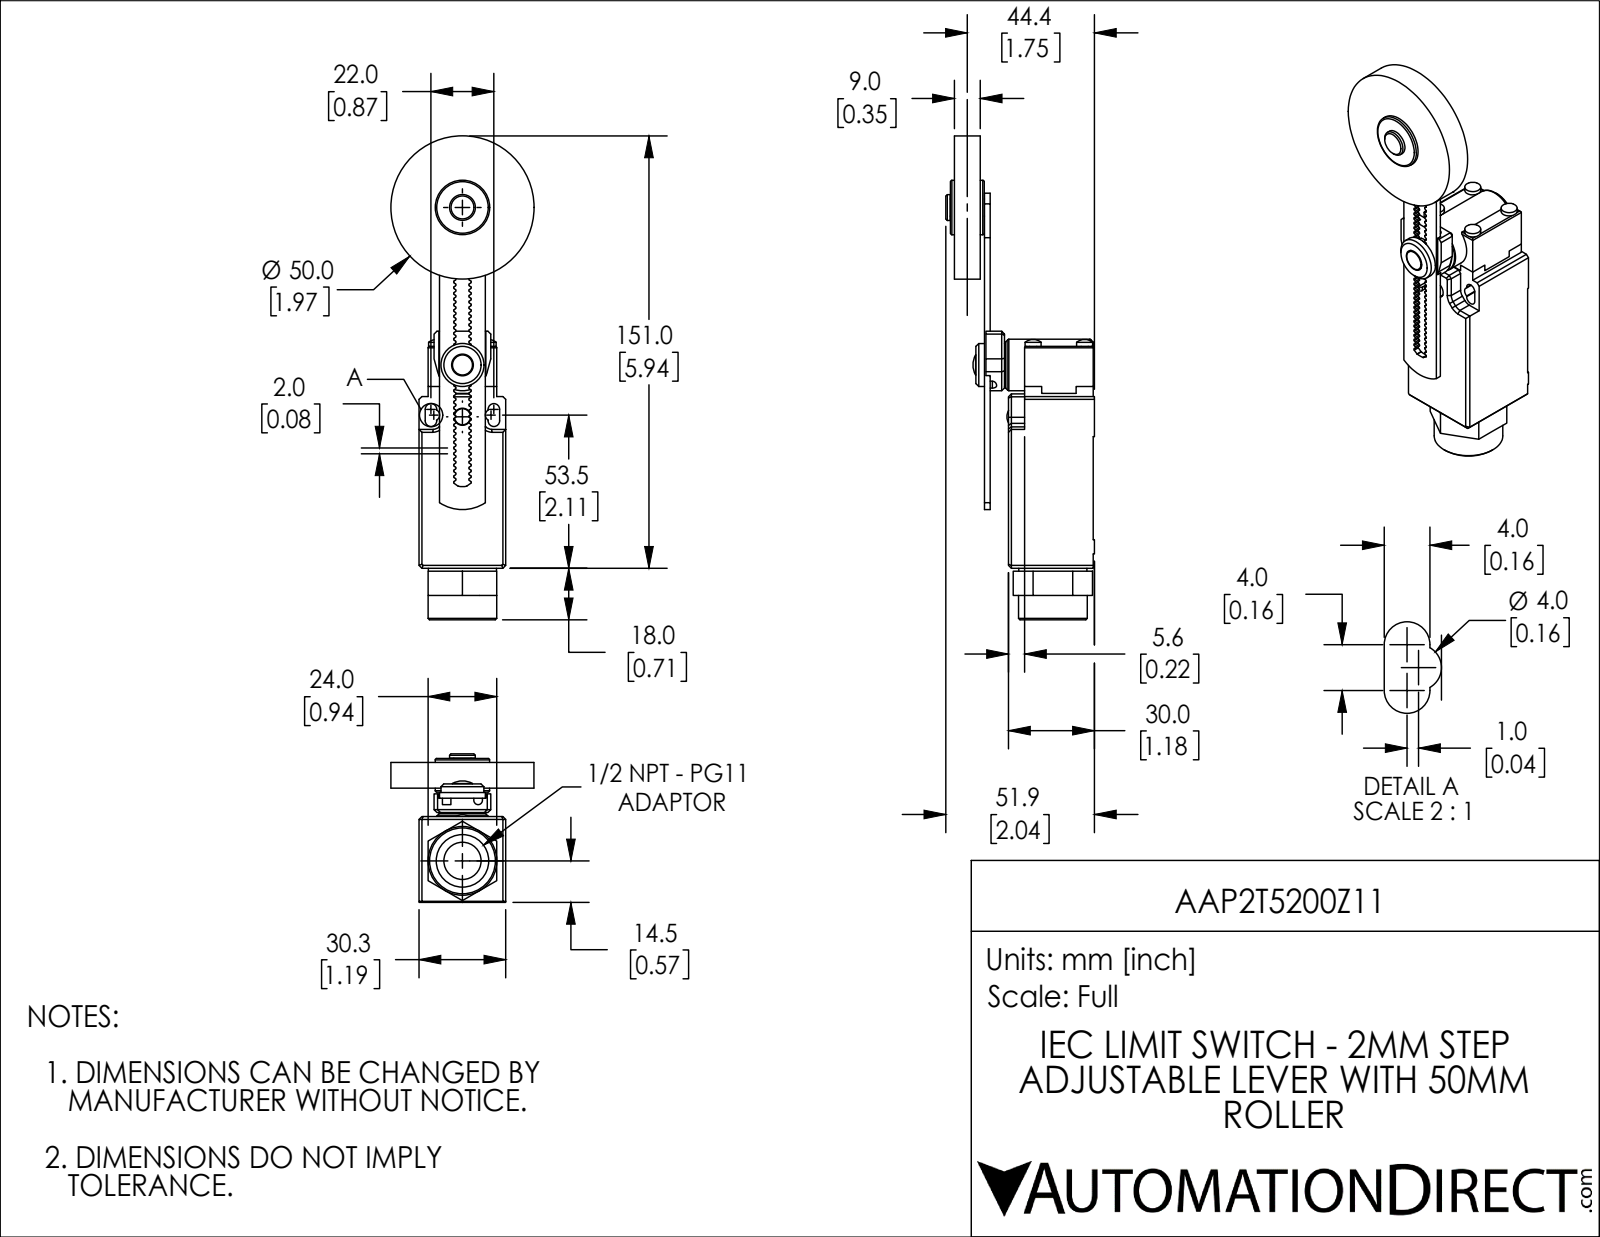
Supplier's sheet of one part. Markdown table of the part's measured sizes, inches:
| quantity | value |
| --- | --- |
| part name | AAP2T5200Z11 |
| STEP written by | SolidWorks 2018 (AUTOMOTIVE_DESIGN) |
| units | inches |
| bodies | 7 solids, 836 faces (345 planar, 447 cylindrical, 44 other) |
| overall size | 6.654 × 2.043 × 1.969 |
| volume | 5.533 in³ |
| surface area | 44.68 in² |
| round holes (diameter × count) | 0.236 × 1, 0.299 × 1, 0.433 × 1, 0.512 × 1, 0.669 × 1, 0.72 × 1, 0.74 × 1, 0.748 × 1 |
| round bosses / shafts (diameter × count) | 0.22 × 5, 1.969 × 1, 0.945 × 1, 0.937 × 1, 0.748 × 1, 0.724 × 1, 0.709 × 1, 0.591 × 1 |
| partial cylindrical surfaces (radius × count) | 0.016 × 166, 0.079 × 6, 0.008 × 4, 0.02 × 4, 0.118 × 4, 0.256 × 2, 0.059 × 1, 0.181 × 1 |
| main face-to-face distances | 0.354, 0.138, 1.909, 0.744, 0.079, 1.555, 1.193, 0.059, 0.413, 0.252 |
| hole center spacings | 0.713 |
